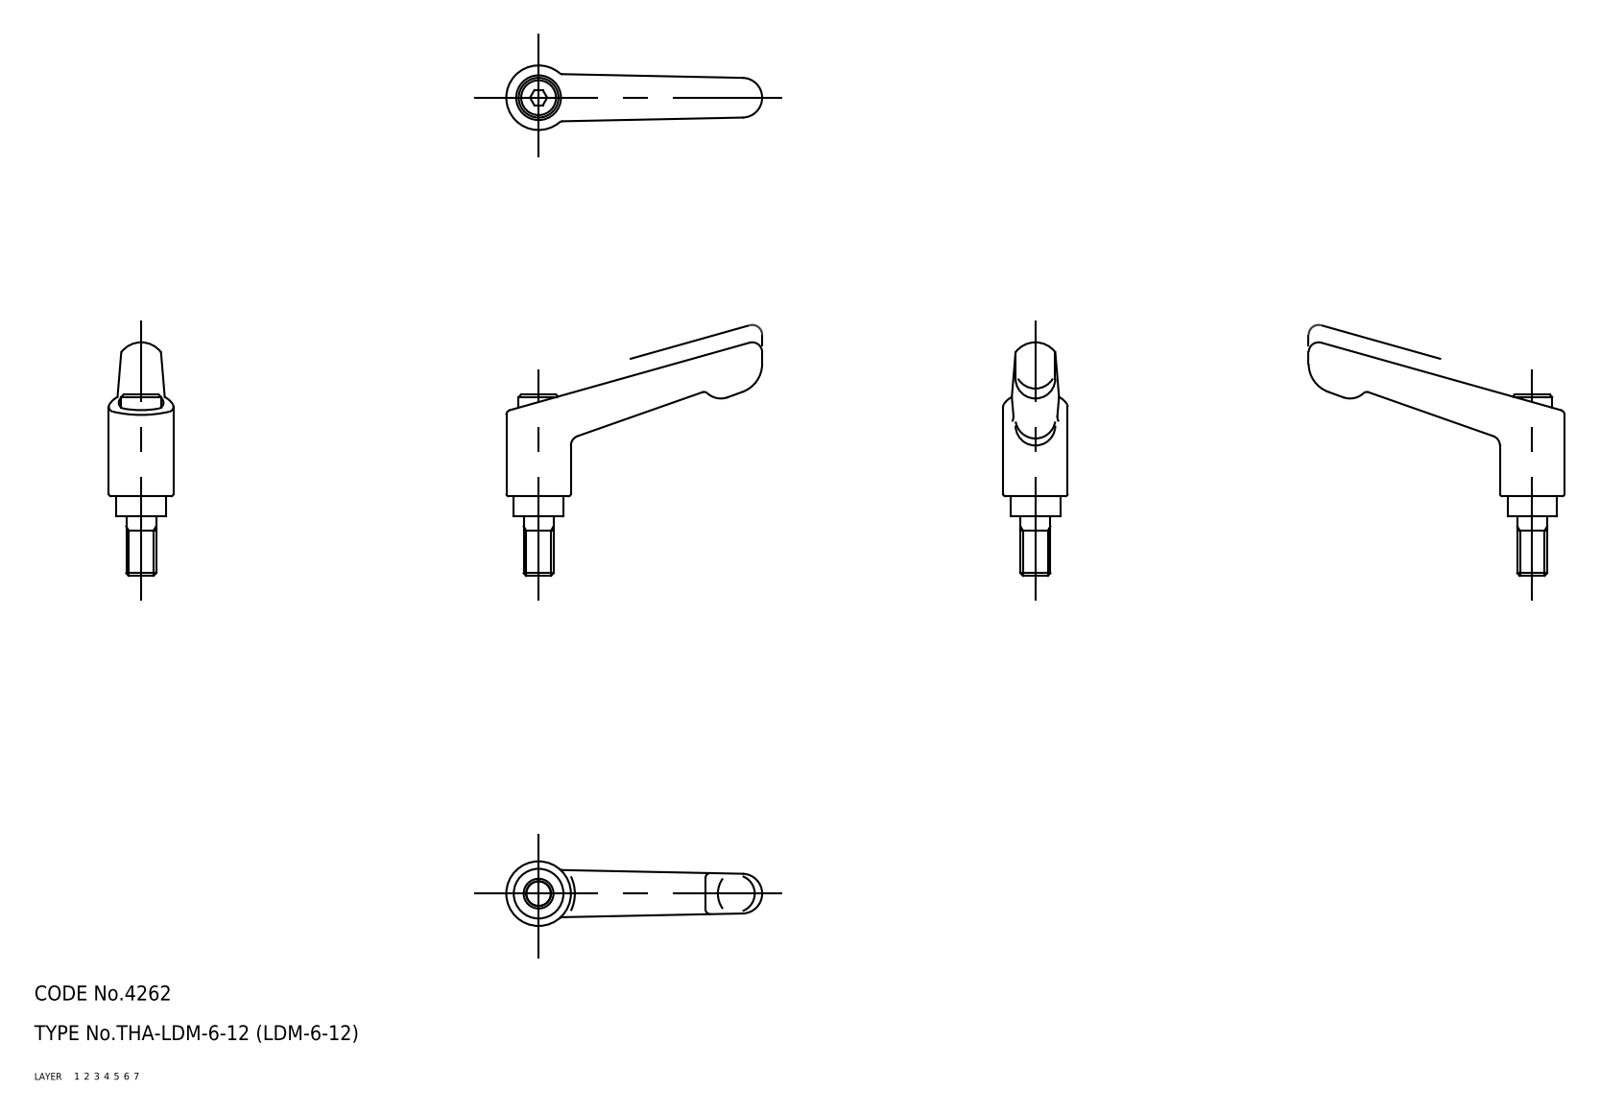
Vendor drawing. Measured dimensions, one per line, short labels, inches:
name: sleeve; screw; handle; LDM_6_12_13002_36
written by: CADfix (AUTOMOTIVE_DESIGN)
unit: in
bodies: 3 solids, 70 faces (0 planar, 0 cylindrical, 70 other)
size: 2.028 × 1.85 × 0.512
volume: 0.334 in³; area: 5.799 in²
